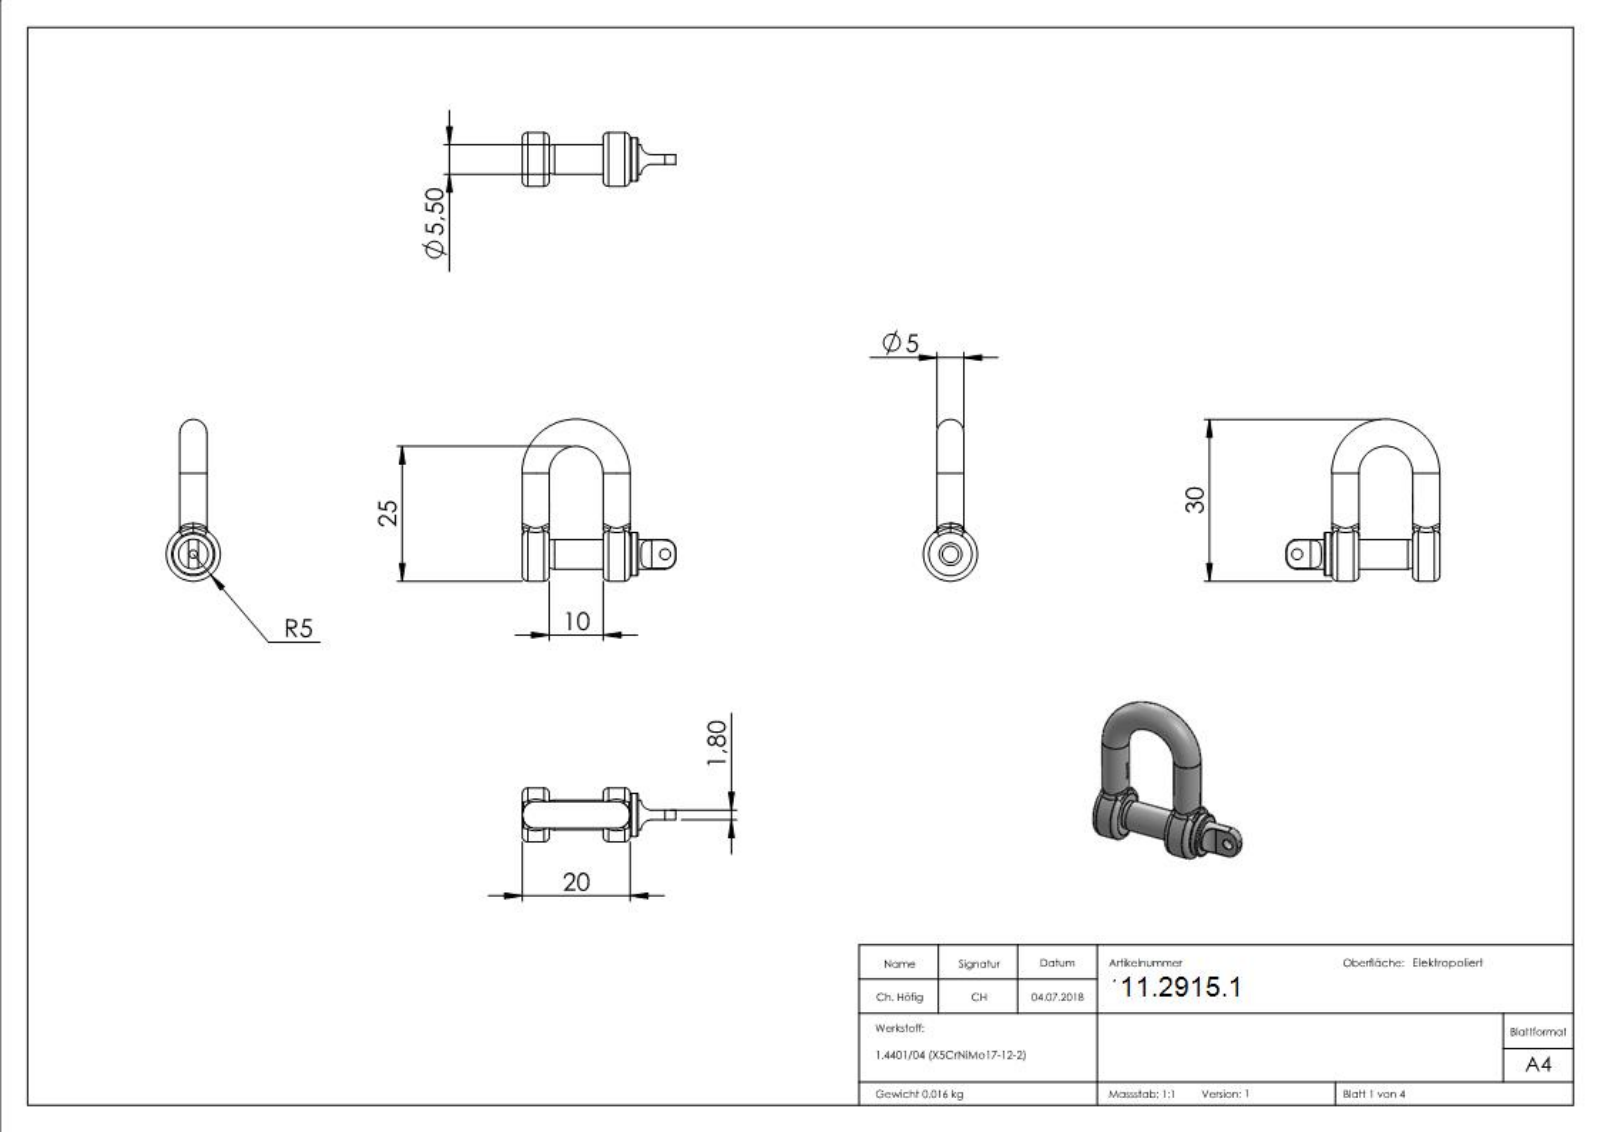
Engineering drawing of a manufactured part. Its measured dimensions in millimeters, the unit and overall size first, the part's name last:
Units: millimetres
Overall size (bounding box): 30 × 28.5 × 10
Round holes (diameter × count): ⌀2 ×1, ⌀4.2 ×1
Round bosses / shafts (diameter × count): ⌀5 ×3, ⌀10 ×1, ⌀8 ×1, ⌀5.5 ×1
Partial cylindrical surfaces — rounded edges, fillets, slot ends (radius × count): R2 ×2, R2.48 ×1
Main face-to-face distances: 5, 15, 20, 10, 21.5, 16.5, 6.5, 1.5, 1.8, 28.5
Volume: 2 031 mm³ · Surface area: 1 850 mm²
Bodies: 2 solids, 304 faces (76 planar, 63 cylindrical, 165 other)
Part name (STEP PRODUCT): 10005005; 1000500X Teil1_10005005 Teil1; 1000500X Teil2_10005005 Teil2
STEP written by: SolidWorks 2015 (CONFIG_CONTROL_DESIGN)
